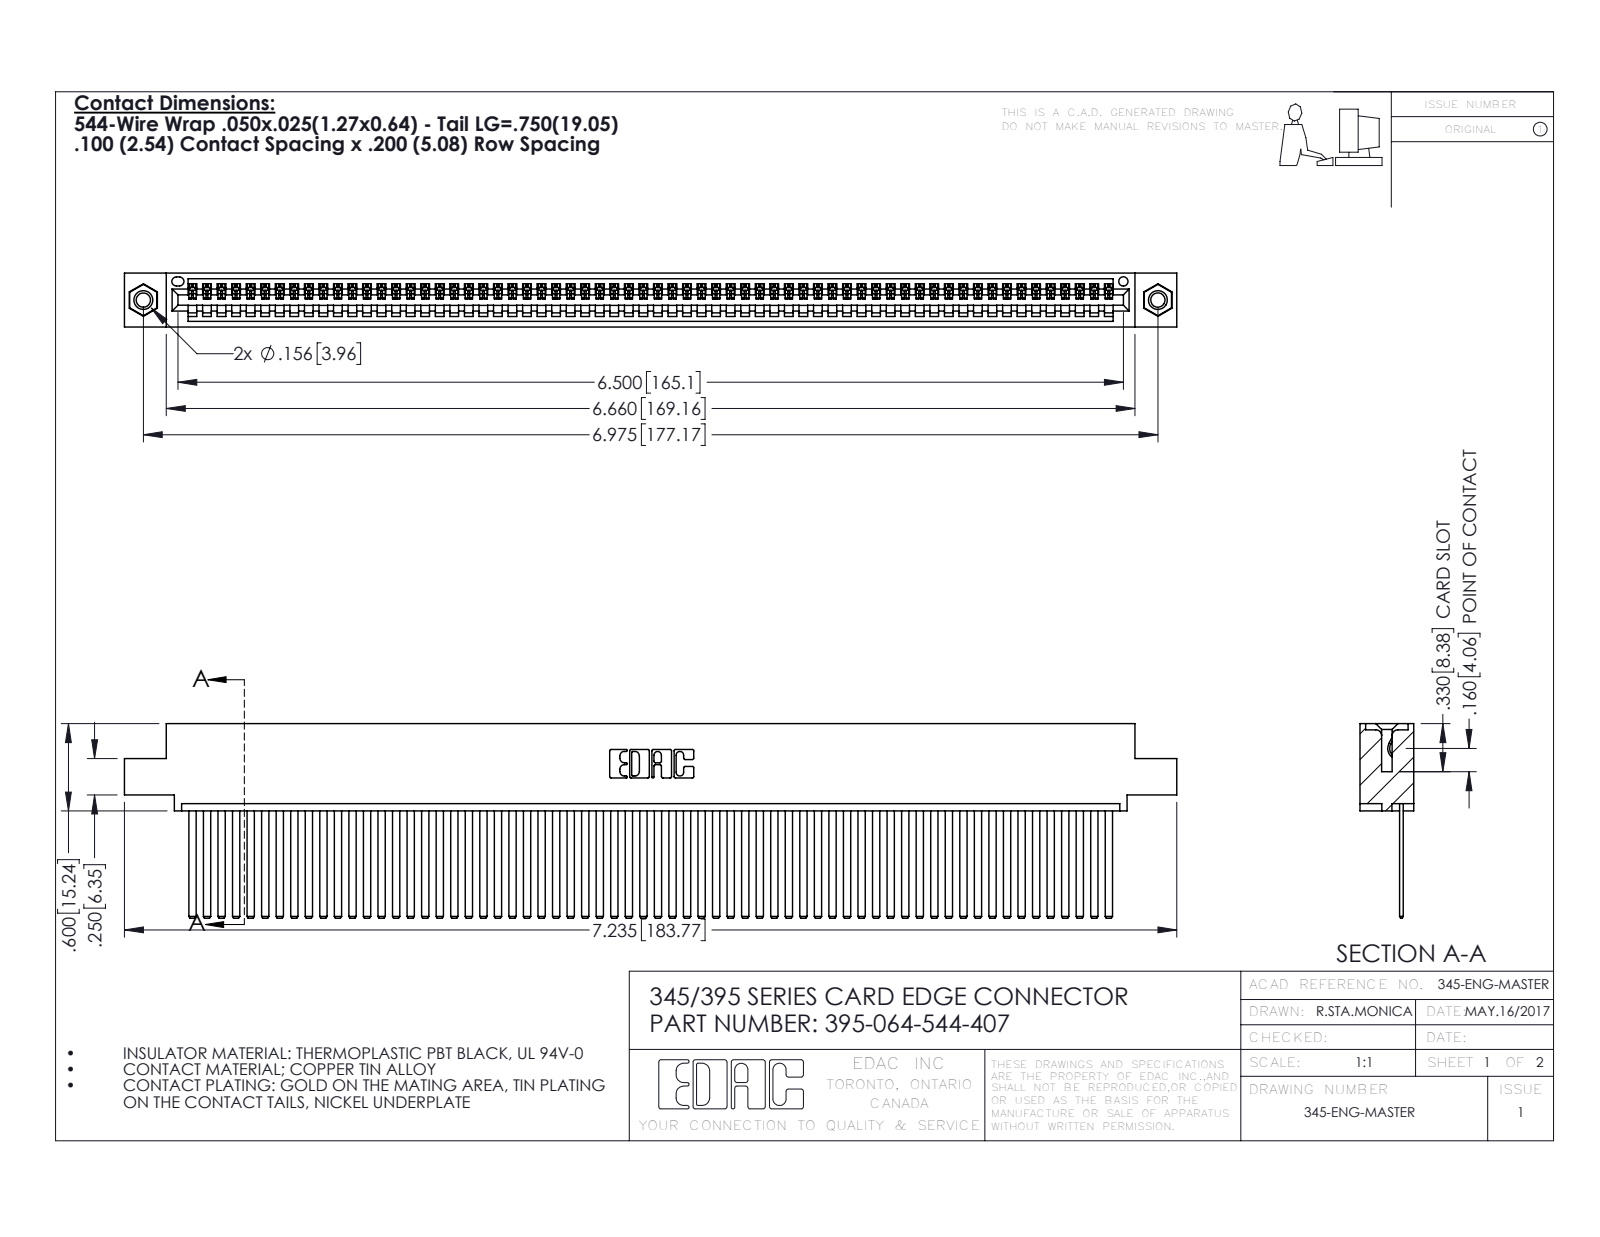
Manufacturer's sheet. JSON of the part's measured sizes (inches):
{"part_name": "345-250-001_345-250-005-103; 345-292-001_345-293-144; 395-064-544-407; 345 Part_0.110 Offset - 0.156 Dia-TI", "step_written_by": "SolidWorks 2016 (CONFIG_CONTROL_DESIGN)", "units": "inches", "bodies": {"solids": 67, "faces": 3518, "planar": 2420, "cylindrical": 1082, "other": 16}, "overall_size": [7.235, 1.337, 0.37], "volume_in3": 1.116, "surface_area_in2": 41.76, "round_holes": [[0.098, 2], [0.125, 2], [0.156, 2], [0.064, 1]], "round_bosses_or_shafts": [[0.155, 2]], "partial_cylinders_radius": [[0.006, 128], [0.01, 22], [0.007, 6], [0.031, 6], [0.026, 3], [0.031, 2], [0.04, 2], [0.014, 1]], "face_to_face_distances": [0.072, 0.298, 0.025, 0.098, 0.272, 0.37, 0.2, 0.225, 0.149, 0.072], "hole_center_spacings": [0.27, 6.739, 6.975]}
